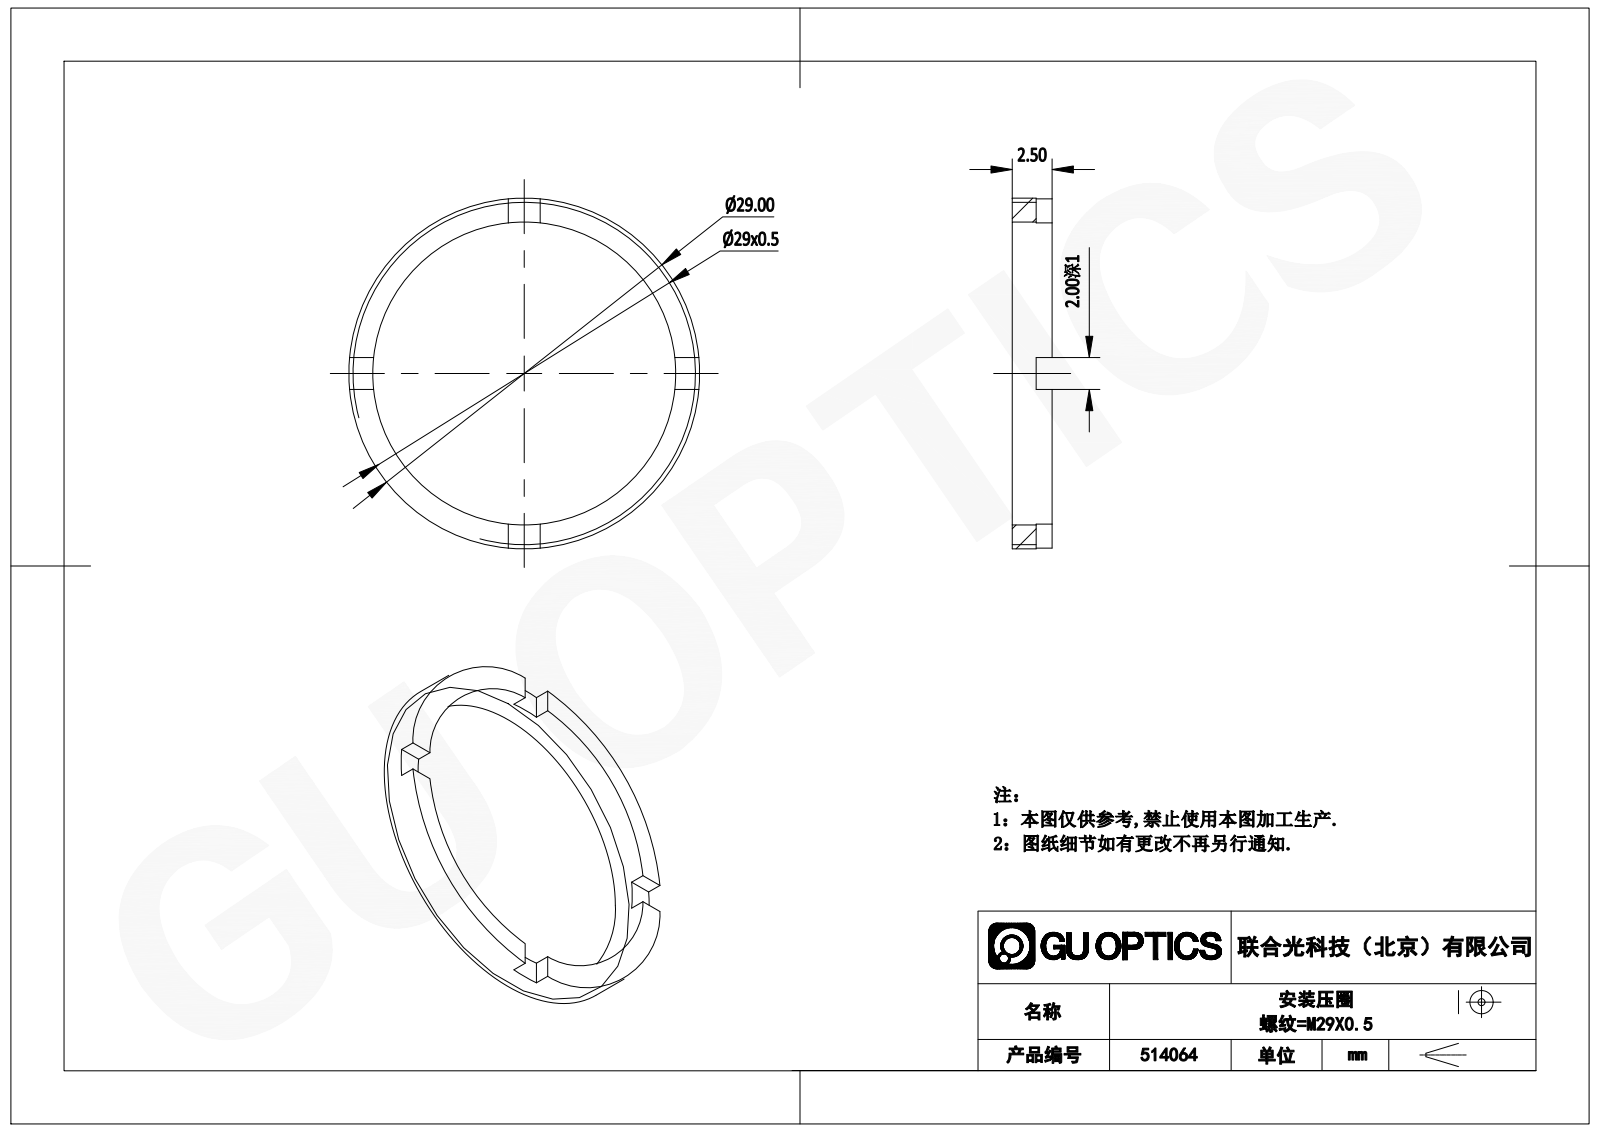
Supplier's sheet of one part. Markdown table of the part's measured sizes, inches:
| quantity | value |
| --- | --- |
| part name | 514064 |
| STEP written by | SolidWorks 2020 (CONFIG_CONTROL_DESIGN) |
| units | inches |
| bodies | 1 solid, 21 faces (17 planar, 4 cylindrical, 0 other) |
| overall size | 1.142 × 1.142 × 0.098 |
| volume | 0.019 in³ |
| surface area | 1.06 in² |
| round holes (diameter × count) | 1.024 × 1 |
| round bosses / shafts (diameter × count) | 1.142 × 1 |
| main face-to-face distances | 0.098, 0.059, 0.039, 0.079 |
